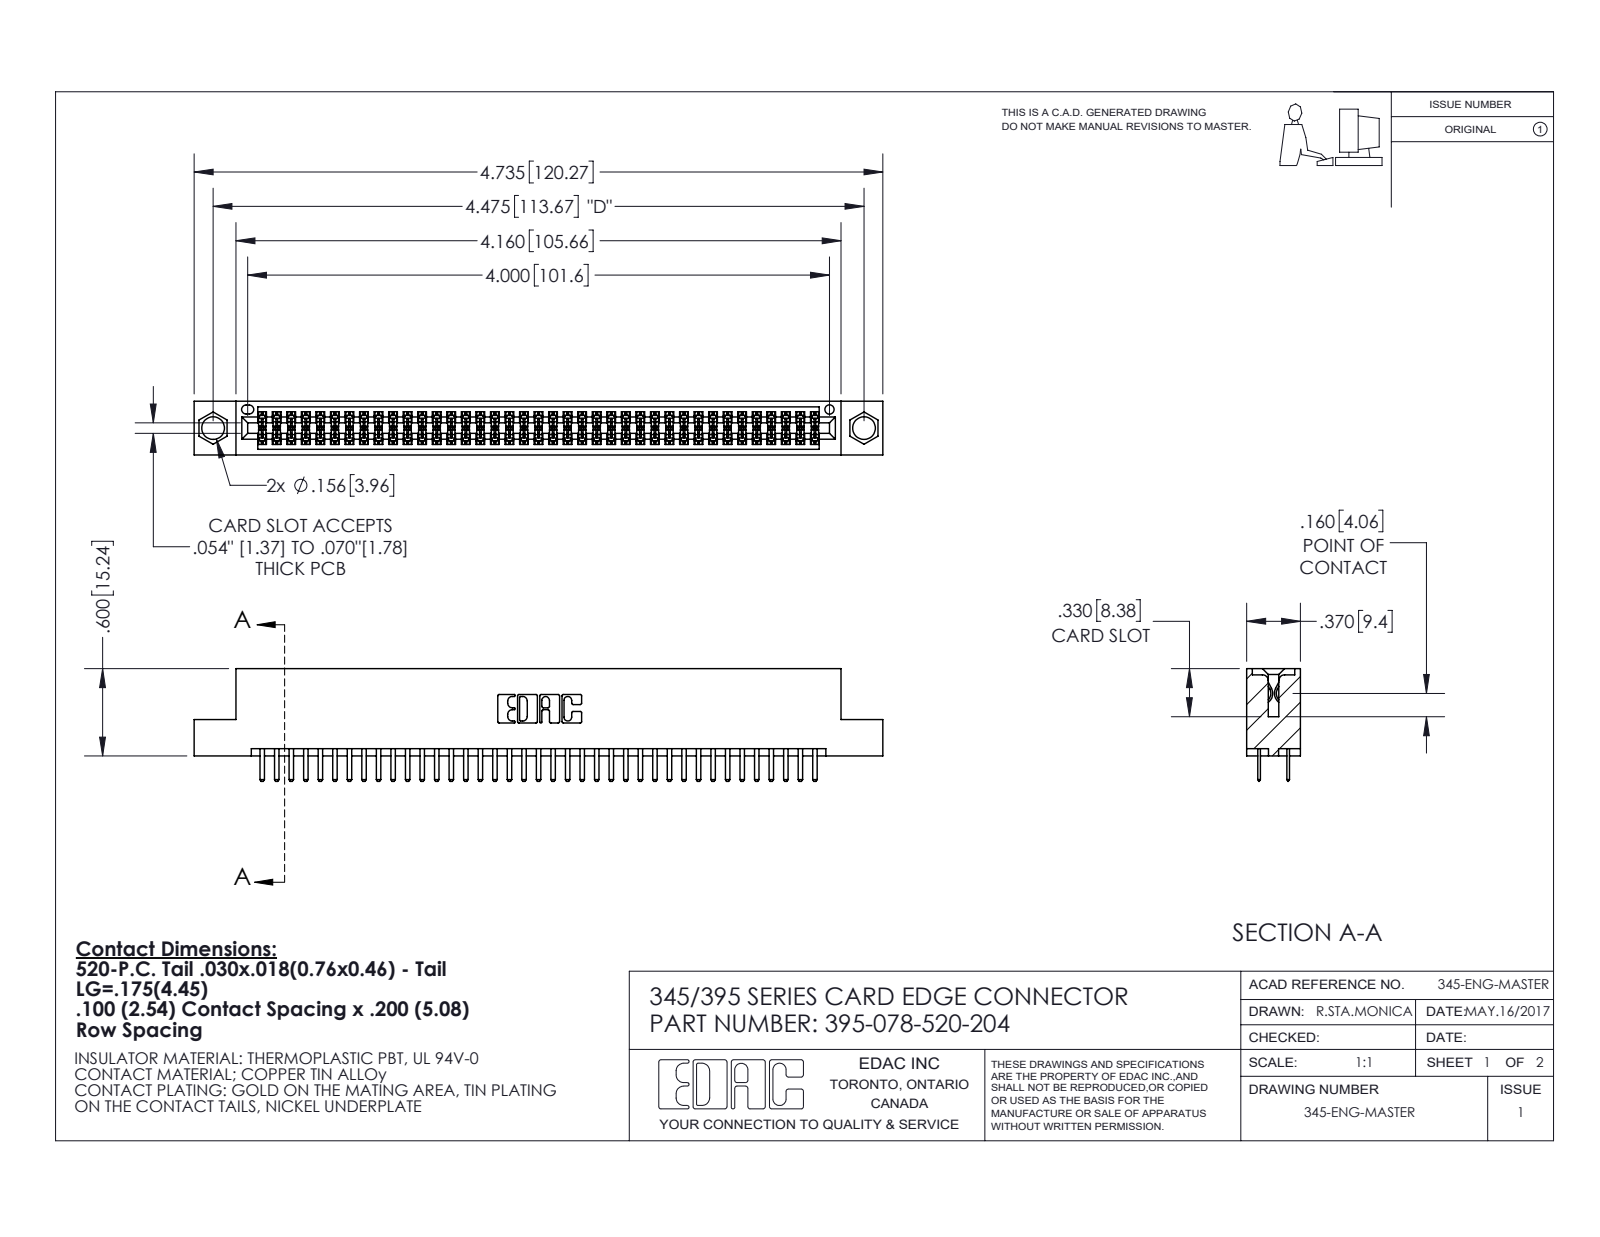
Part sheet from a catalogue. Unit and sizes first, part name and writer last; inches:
Units: inches
Overall size (bounding box): 4.735 × 0.775 × 0.37
Round holes (diameter × count): ⌀0.156 ×2, ⌀0.064 ×1
Partial cylindrical surfaces — rounded edges, fillets, slot ends (radius × count): R0.006 ×156, R0.01 ×82, R0.01 ×22, R0.007 ×6, R0.031 ×6, R0.026 ×3, R0.014 ×2, R0.019 ×2
Main face-to-face distances: 0.072, 0.298, 0.2, 0.37, 0.098, 0.272, 0.025, 0.225, 0.022, 0.072
Hole centre spacings: 0.27, 4.239, 4.475
Volume: 0.703 in³ · Surface area: 25.95 in²
Bodies: 79 solids, 4352 faces (2824 planar, 1528 cylindrical, 0 other)
Part name (STEP PRODUCT): 395-078-520-204; 345 Part_Flush Mounting Lugs - 0.156 Dia-TI; 345-292-001_345-293-120
STEP written by: SolidWorks 2020 (CONFIG_CONTROL_DESIGN)
